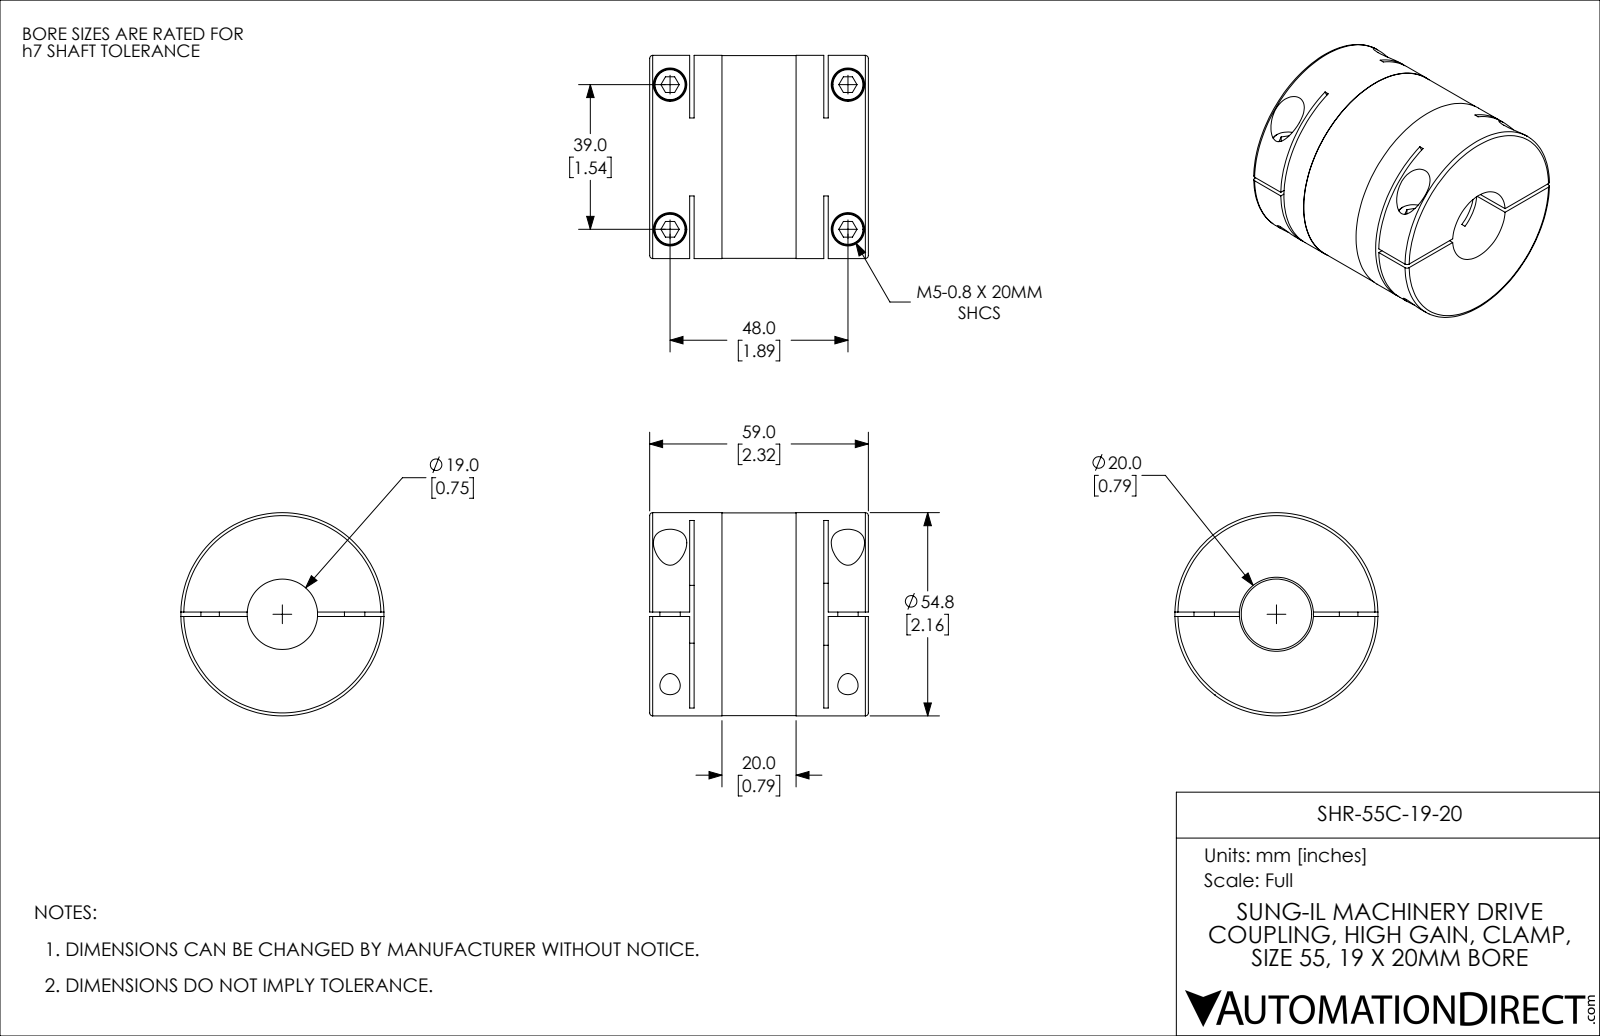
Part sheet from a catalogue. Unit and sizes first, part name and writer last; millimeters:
Units: millimetres
Overall size (bounding box): 59 × 54.8 × 54.8
Round holes (diameter × count): ⌀5.5 ×4, ⌀9 ×4, ⌀19 ×1, ⌀20 ×1, ⌀22 ×1
Round bosses / shafts (diameter × count): ⌀8.5 ×4, ⌀5 ×2, ⌀54.8 ×1, ⌀54.7 ×1
Partial cylindrical surfaces — rounded edges, fillets, slot ends (radius × count): R60 ×2
Main face-to-face distances: 1.2, 12, 47, 10.8, 48.2, 36.2, 59, 35, 37.4, 19.5
Hole centre spacings: 39, 48, 61.85
Volume: 112 439 mm³ · Surface area: 28 537 mm²
Bodies: 1 solid, 144 faces (70 planar, 58 cylindrical, 16 other)
Part name (STEP PRODUCT): SHR-55C-19-20
STEP written by: SolidWorks 2021 (CONFIG_CONTROL_DESIGN)
